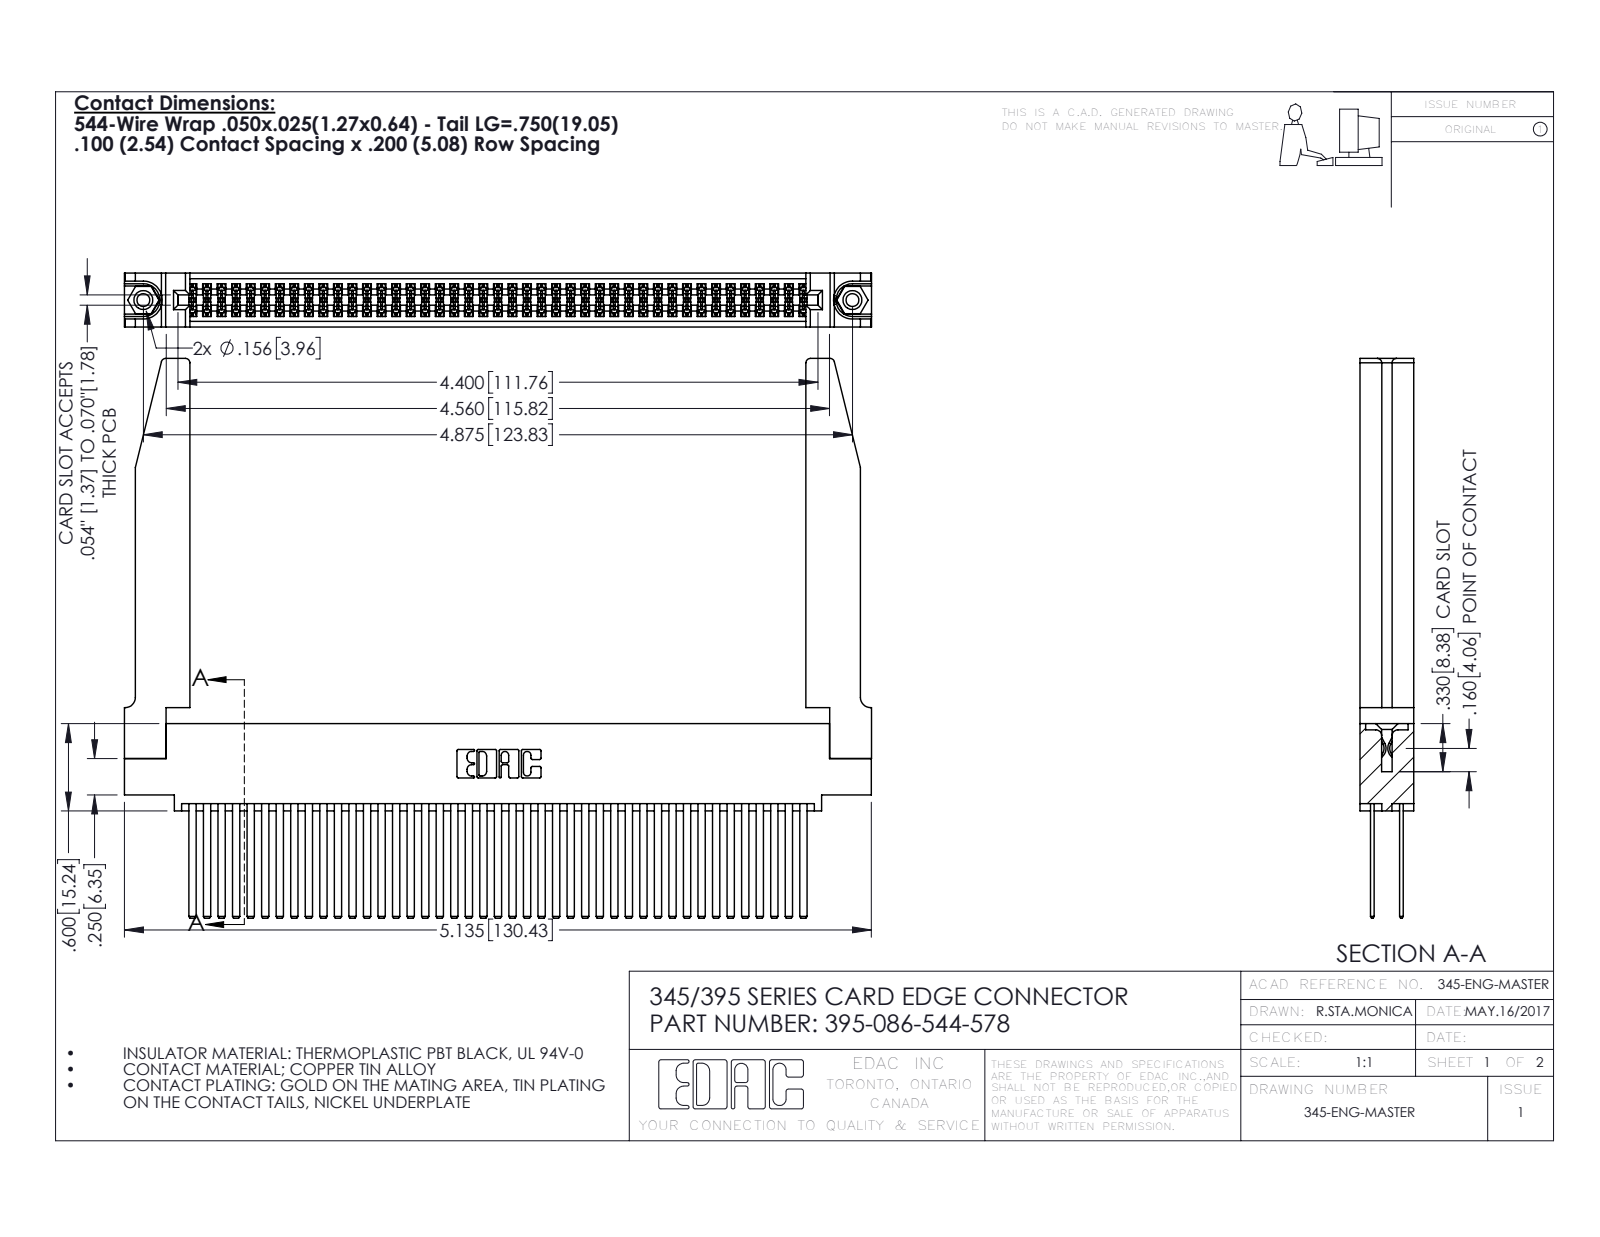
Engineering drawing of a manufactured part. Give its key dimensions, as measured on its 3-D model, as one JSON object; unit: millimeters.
{"part_name": "345 Part_0.110 Offset - 0.156 Dia-TH; 345-250-001_345-250-001-102; 345-220-078_345-220-078; 395-086-544-578 (+1 more)", "step_written_by": "SolidWorks 2016 (CONFIG_CONTROL_DESIGN)", "units": "millimeters", "bodies": {"solids": 91, "faces": 4148, "planar": 2720, "cylindrical": 1376, "other": 52}, "overall_size": [130.5, 97.7, 9.4], "volume_mm3": 21580, "surface_area_mm2": 30900, "round_holes": [[2.3, 2], [3.2, 2], [4, 2], [1.6, 1]], "round_bosses_or_shafts": [[3.9, 2]], "partial_cylinders_radius": [[0.2, 129], [0.3, 22], [0.8, 8], [0.2, 6], [0.8, 6], [0.7, 3], [0.4, 2], [0.5, 2]], "face_to_face_distances": [1.8, 7.6, 2.5, 6.9, 0.6, 5.1, 9.4, 5.7, 4.4, 3.8], "hole_center_spacings": [6.9, 117.8, 123.8]}
